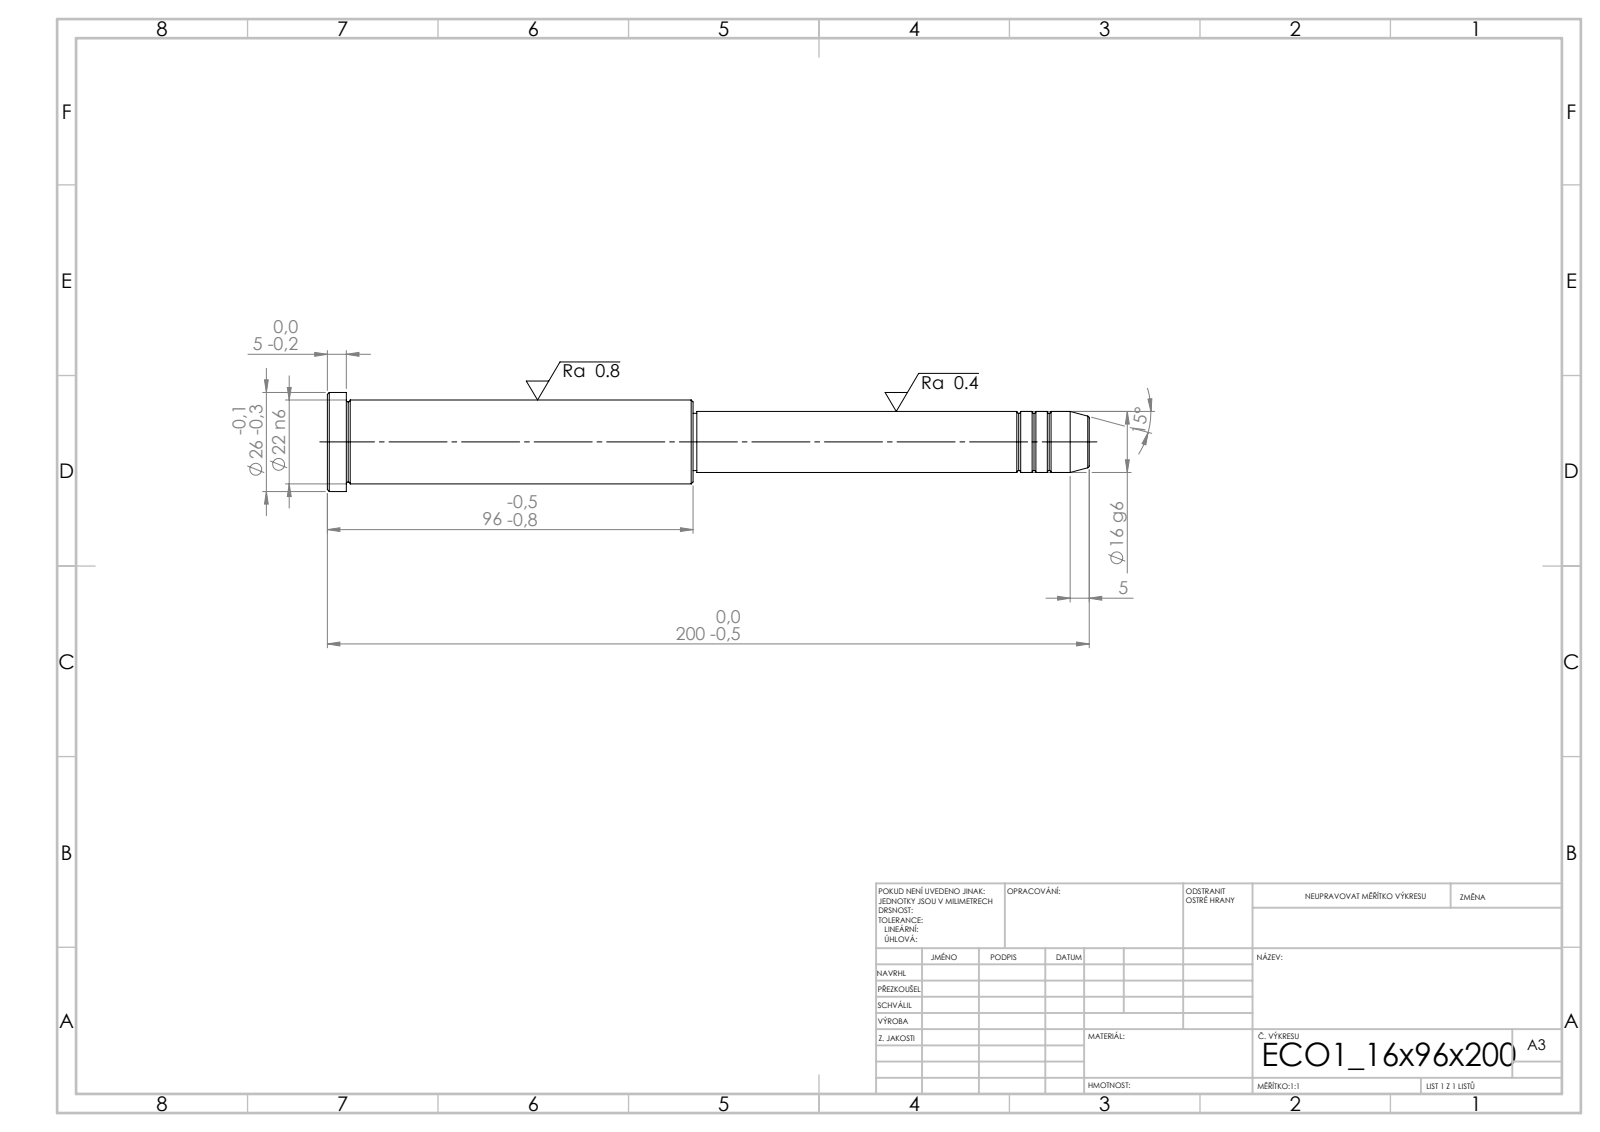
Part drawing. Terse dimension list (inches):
written by: SolidWorks 2019 (CONFIG_CONTROL_DESIGN)
unit: in
bodies: 1 solid, 43 faces (5 planar, 14 cylindrical, 24 other)
size: 7.874 × 1.024 × 1.024
volume: 3.531 in³; area: 20.18 in²
bosses: 1× ⌀1.024, 1× ⌀0.866, 1× ⌀0.63, 1× ⌀0.591
face distances: 3.78, 3.583, 0.197, 4.094, 7.677, 7.874, 4.055, 0.039, 3.622, 3.819
